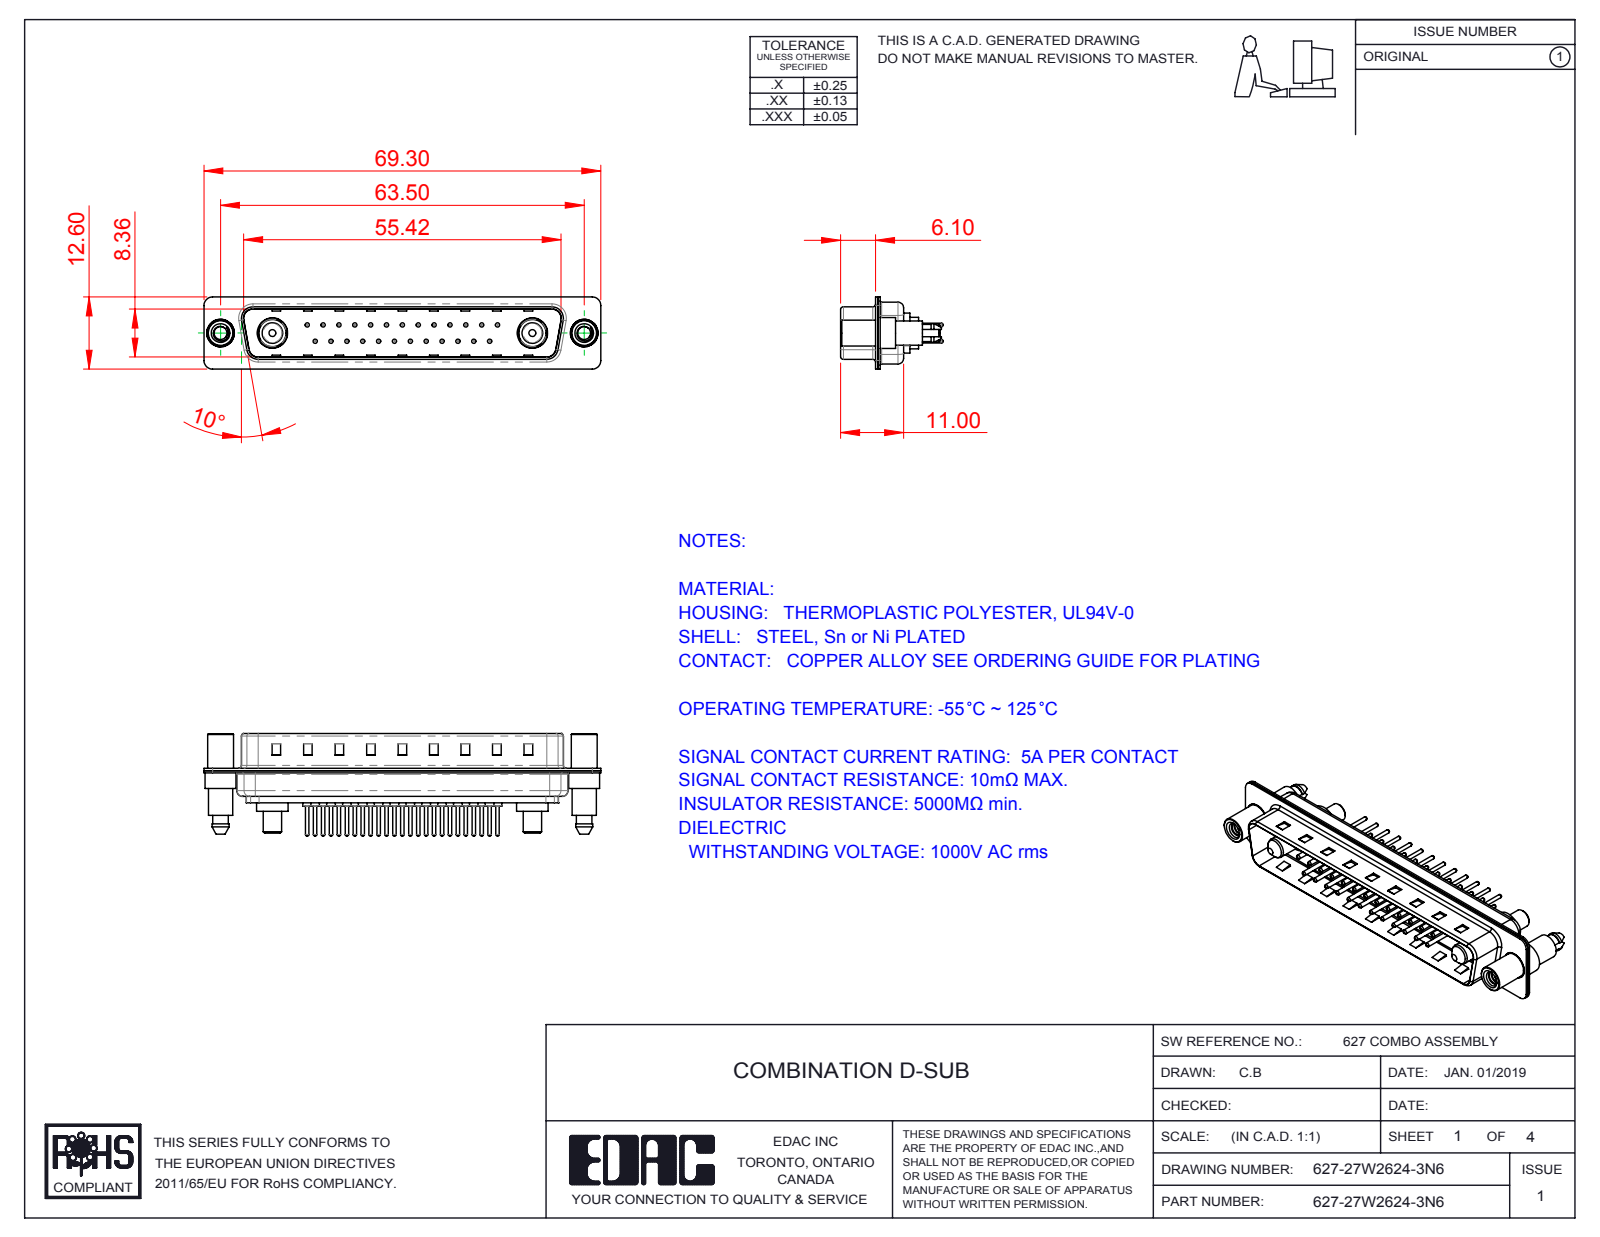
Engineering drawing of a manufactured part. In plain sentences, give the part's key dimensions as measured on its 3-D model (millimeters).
The part is named "627-27W2624-3N6; 627Combo Housing_27W2; 627Combo Threaded Standoff and Boardlock_6; 627Combo Shell Front_37 Contacts (+4 more)". Its 3-D file was written by "SolidWorks 2016 (CONFIG_CONTROL_DESIGN)". It is 34 solids with 1469 faces: 416 planar, 557 cylindrical and 496 other. Overall it measures 69.3 by 17.9 by 12.6 millimeters. Its volume is 4 249 cubic millimeters and its surface area 9 535 square millimeters. Round holes: 25 of diameter 0.75, 25 of diameter 1.6, 25 of diameter 2, 2 of diameter 2.26, 2 of diameter 4, 2 of diameter 4.8, 2 of diameter 4.85, 2 of diameter 5.3. Round bosses or shafts: 25 of diameter 1.5, 25 of diameter 0.6, 2 of diameter 5.5, 2 of diameter 5.4, 2 of diameter 5.2, 2 of diameter 4.9, 2 of diameter 4.75, 2 of diameter 4.5. Partial cylindrical surfaces (rounded edges, fillets, slot ends): 18 of radius 1.5, 12 of radius 2, 10 of radius 1.6, 8 of radius 0.5, 4 of radius 0.25, 4 of radius 0.6, 4 of radius 0.65, 4 of radius 0.9. The main face-to-face distances are 0.4, 0.82, 9.58, 8.76, 1.5, 5.6, 1.22, 9.98, 0.42, 9.18. The hole center spacings are 3.16, 2.77, 5.54, 8.31, 5.03, 7.48, 11.08, 5.04.
